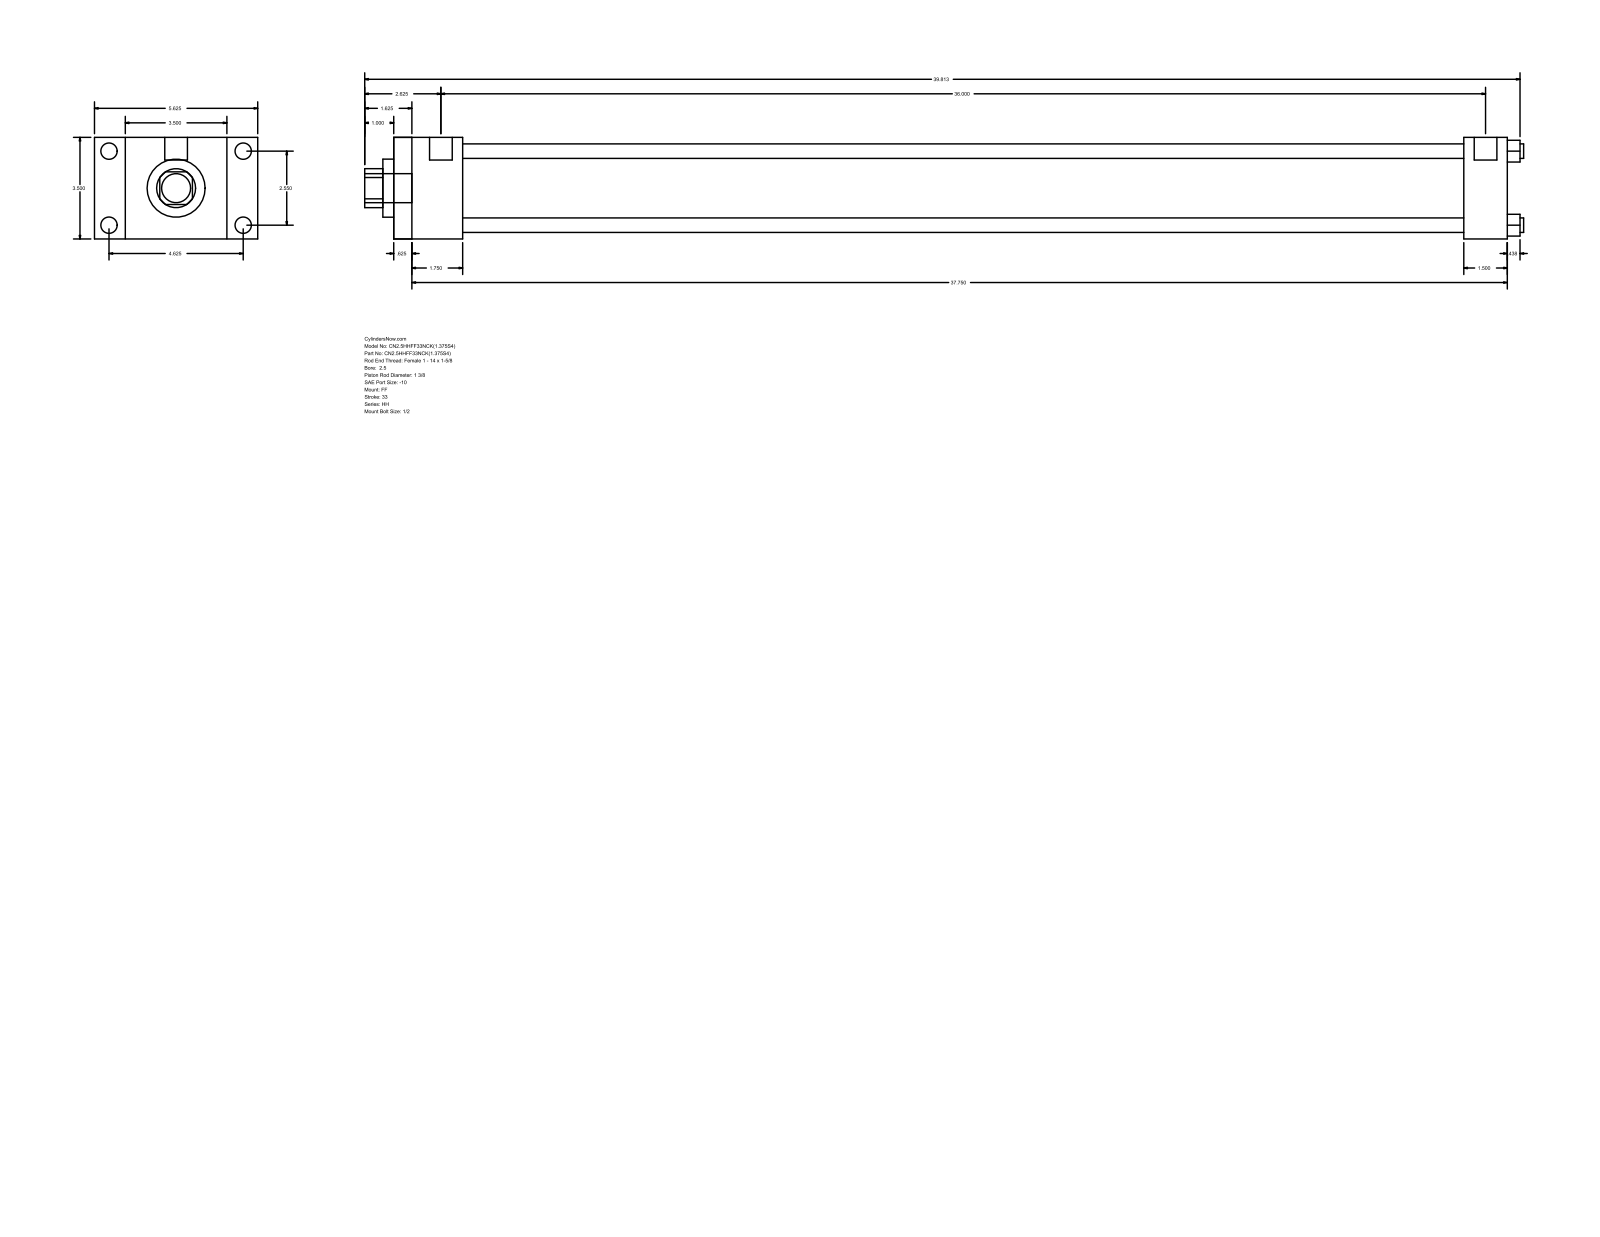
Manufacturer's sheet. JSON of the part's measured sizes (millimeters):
{"part_name": "HH_FF__0250_1.375", "step_written_by": "GSSL Pune (CONFIG_CONTROL_DESIGN)", "units": "millimeters", "bodies": {"solids": 0, "faces": 92, "planar": 64, "cylindrical": 28, "other": 0}, "overall_size": [1014.41, 142.88, 88.9], "round_holes": [[12.7, 4], [34.92, 1], [50.8, 1], [73.03, 1]], "round_bosses_or_shafts": [[14.3, 4], [5.56, 4], [19.84, 2], [25.4, 1]], "partial_cylinders_radius": [[17.06, 1]], "face_to_face_distances": [88.9, 974.72, 15.87, 958.85, 60.32, 44.45, 914.4, 936.62, 920.75, 876.3], "hole_center_spacings": [45.79, 64.76, 91.58]}
